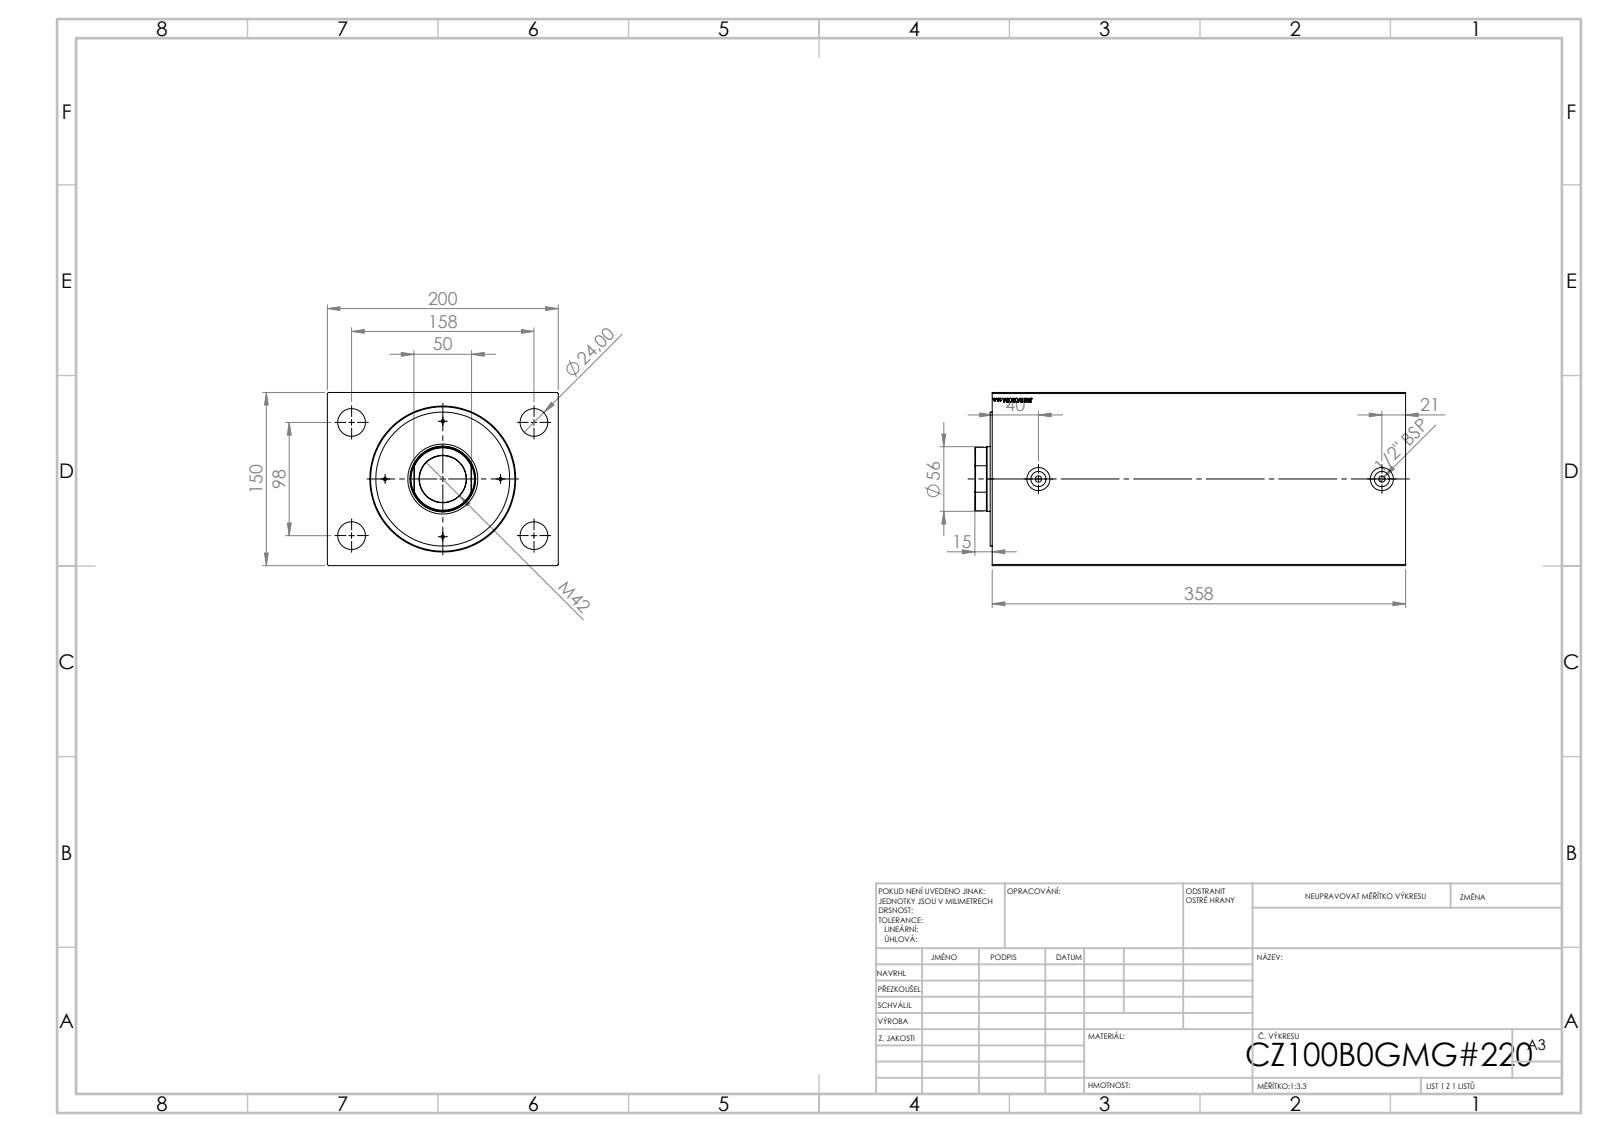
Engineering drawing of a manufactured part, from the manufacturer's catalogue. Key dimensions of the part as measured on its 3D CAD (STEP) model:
Part name (STEP PRODUCT): V500CZ_B_VC; V500CZ
STEP written by: SolidWorks 2019 (CONFIG_CONTROL_DESIGN)
Units: millimetres
Bodies: 3 solids, 874 faces (400 planar, 58 cylindrical, 416 other)
Overall size (bounding box): 373 × 200 × 150
Volume: 9 394 000 mm³ · Surface area: 553 478 mm²
Round holes (diameter × count): ⌀3 ×4, ⌀24 ×4, ⌀5.5 ×2, ⌀13.16 ×2, ⌀20 ×2, ⌀36 ×1, ⌀40.5 ×1, ⌀56 ×1, ⌀57 ×1, ⌀100 ×1, ⌀125 ×1
Round bosses / shafts (diameter × count): ⌀116 ×1
Partial cylindrical surfaces — rounded edges, fillets, slot ends (radius × count): R27.5 ×1
Main face-to-face distances: 150, 200, 358, 324.7, 33.3, 15, 1.8, 13.2, 311.5, 344.8
Hole centre spacings: 50, 56.94, 70.71, 79.01, 92.96, 126.66, 137.99, 98
